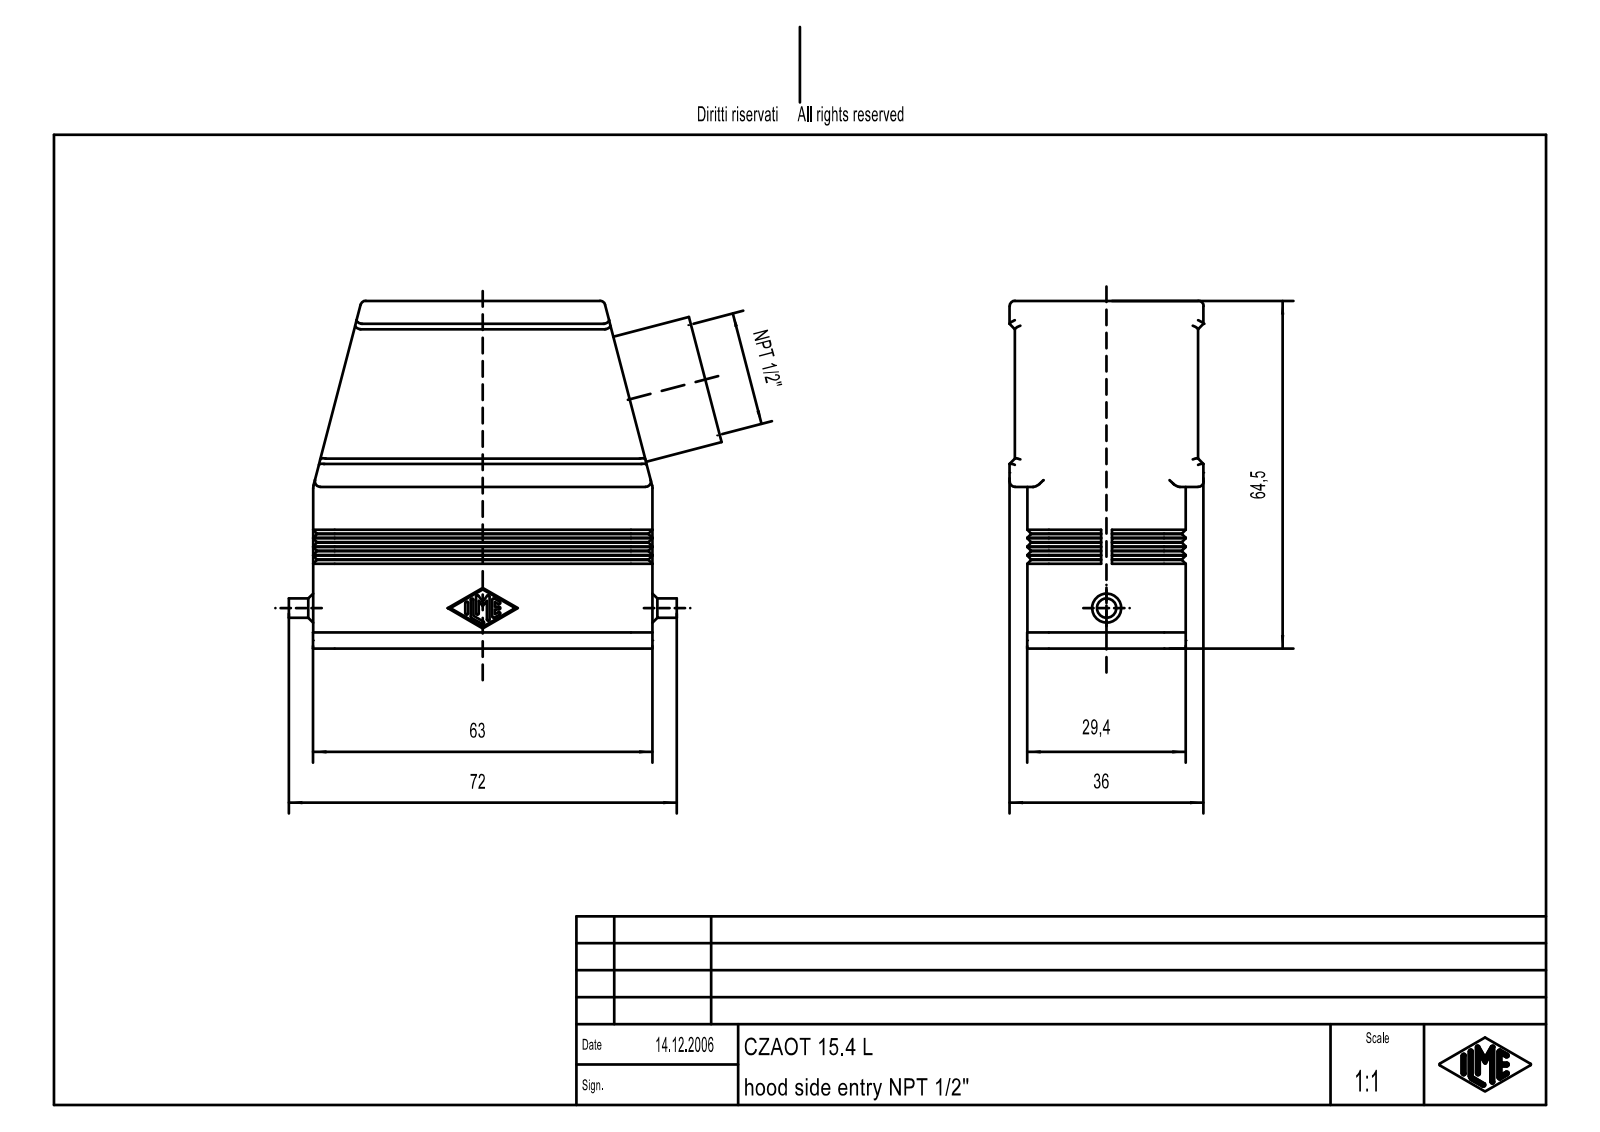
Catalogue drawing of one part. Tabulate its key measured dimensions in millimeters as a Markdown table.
| quantity | value |
| --- | --- |
| part name | MSBO7115 |
| STEP written by | Creo Elements/Direct Modeling 18.0B 02-Dec-2011 (C) Parametric Technology GmbH (AUTOMOTIVE_DESIGN) |
| units | millimeters |
| bodies | 0 solids, 362 faces (188 planar, 116 cylindrical, 58 other) |
| overall size | 80.32 × 64.5 × 36 |
| round holes (diameter × count) | 2.46 × 4, 3.5 × 4 |
| round bosses / shafts (diameter × count) | 24 × 1, 3.6 × 1 |
| partial cylindrical surfaces (radius × count) | 1 × 28, 0.25 × 14, 2 × 6, 1.25 × 4, 3.3 × 4, 4 × 4, 12 × 1 |
| main face-to-face distances | 3, 26.4, 23.4, 2.3, 28.7, 5.3, 31.7, 29.4, 10, 34 |
| hole center spacings | 16, 49.5, 52.02 |
